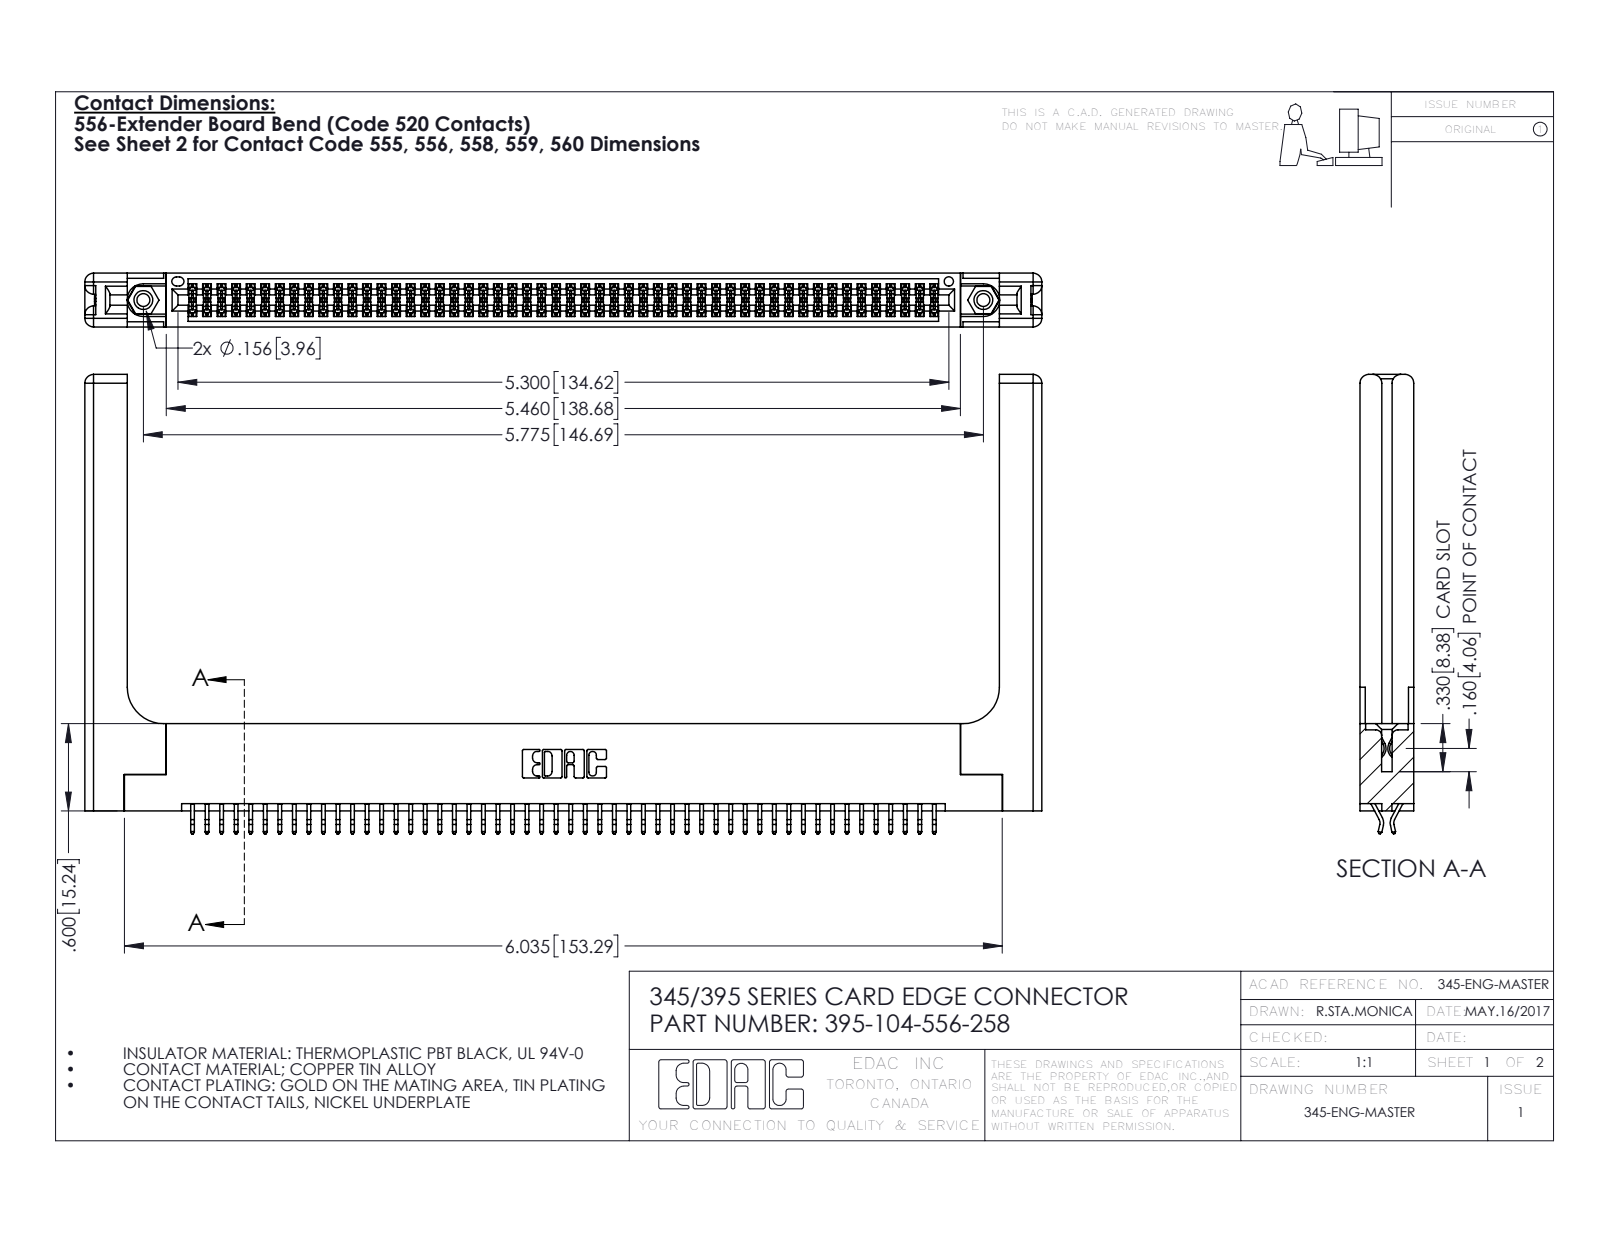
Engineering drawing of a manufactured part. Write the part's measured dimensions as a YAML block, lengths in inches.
part_name: "345-220-058_345-220-058; 395-104-556-258; 345-250-001_345-250-001-102; 345-292-001_556 Tail (+1 more)"
step_written_by: "SolidWorks 2016 (CONFIG_CONTROL_DESIGN)"
units: inches
bodies: {solids: 109, faces: 6206, planar: 4076, cylindrical: 2070, other: 60}
overall_size: [6.579, 3.157, 0.37]
volume: 1.513
surface_area: 45.4
round_holes:
  - {diameter: 0.089, count: 2}
  - {diameter: 0.125, count: 2}
  - {diameter: 0.156, count: 2}
  - {diameter: 0.064, count: 1}
round_bosses_or_shafts:
  - {diameter: 0.155, count: 2}
partial_cylinders:
  - {radius: 0.006, count: 156}
  - {radius: 0.01, count: 22}
  - {radius: 0.06, count: 16}
  - {radius: 0.007, count: 6}
  - {radius: 0.031, count: 6}
  - {radius: 0.026, count: 3}
  - {radius: 0.01, count: 2}
  - {radius: 0.014, count: 2}
face_to_face_distances: [0.072, 0.298, 0.37, 0.2, 0.025, 0.098, 0.272, 0.225, 0.148, 0.15]
hole_center_spacings: [0.27, 5.539, 5.775]
